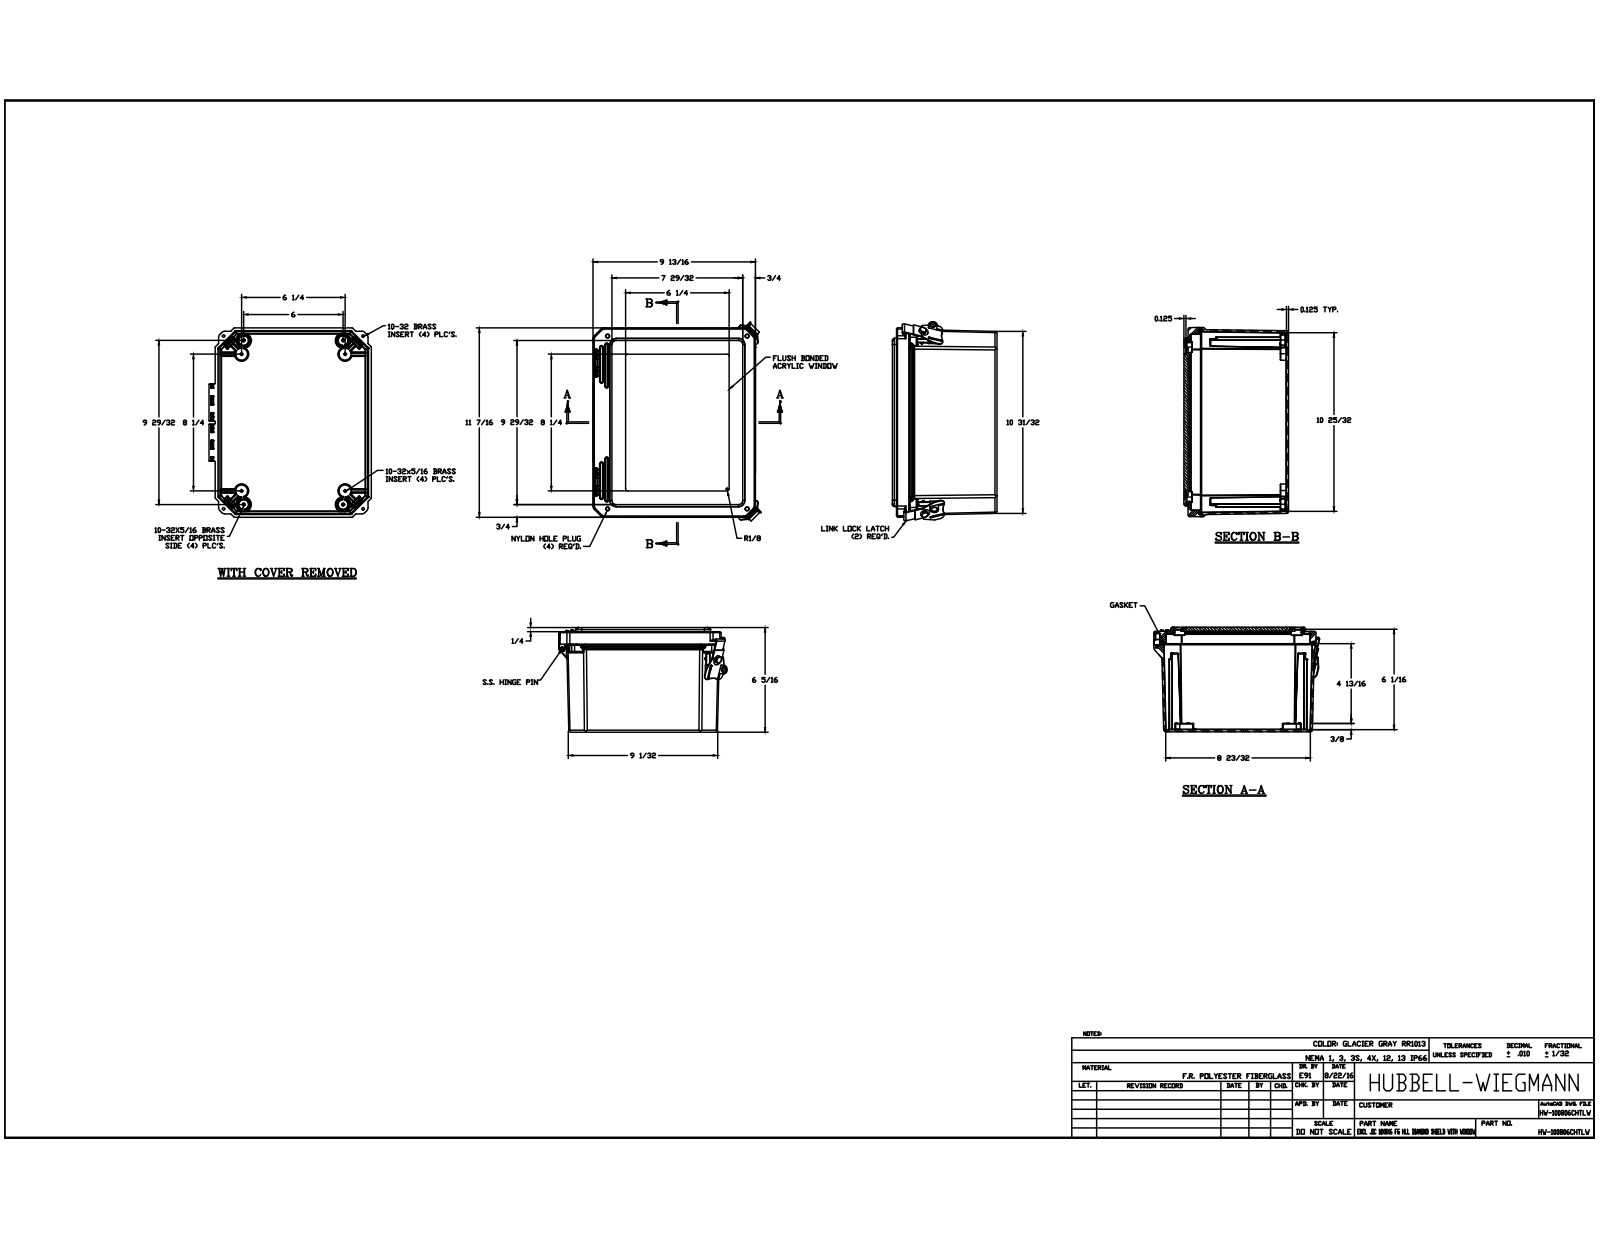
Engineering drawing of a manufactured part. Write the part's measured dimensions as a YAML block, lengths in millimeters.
part_name: "DSW100806HLL_STP; DS100806BOX; BRASS INSERT-(_1; BRASS INSERT-(_2 (+7 more)"
step_written_by: "Autodesk Inventor 2017 (AUTOMOTIVE_DESIGN)"
units: millimeters
bodies: {solids: 32, faces: 2270, planar: 762, cylindrical: 896, other: 612}
overall_size: [313.16, 260.47, 160.33]
volume: 1266000
surface_area: 670818
round_holes:
  - {diameter: 3.96, count: 12}
  - {diameter: 3.86, count: 8}
  - {diameter: 2.49, count: 4}
  - {diameter: 3.81, count: 4}
  - {diameter: 6.4, count: 4}
  - {diameter: 6.43, count: 4}
  - {diameter: 1.27, count: 2}
  - {diameter: 3.05, count: 2}
  - {diameter: 3.48, count: 2}
  - {diameter: 5.56, count: 2}
  - {diameter: 5.77, count: 2}
  - {diameter: 7.94, count: 2}
round_bosses_or_shafts:
  - {diameter: 6.25, count: 12}
  - {diameter: 22.1, count: 4}
  - {diameter: 5.3, count: 4}
  - {diameter: 5.08, count: 4}
  - {diameter: 3.43, count: 3}
  - {diameter: 15.24, count: 2}
  - {diameter: 11.05, count: 2}
  - {diameter: 1.27, count: 2}
partial_cylinders:
  - {radius: 0.25, count: 177}
  - {radius: 0.13, count: 80}
  - {radius: 0.51, count: 57}
  - {radius: 0.76, count: 45}
  - {radius: 3.17, count: 38}
  - {radius: 0.99, count: 28}
  - {radius: 1.59, count: 26}
  - {radius: 0.76, count: 24}
face_to_face_distances: [3.17, 157.16, 3.23, 3.2, 160.33, 154.62, 151.45, 5.71, 2.54, 153.99]
hole_center_spacings: [238.73, 248.32, 259.82, 20.15, 21.1, 31.49, 39.01, 156.97]
